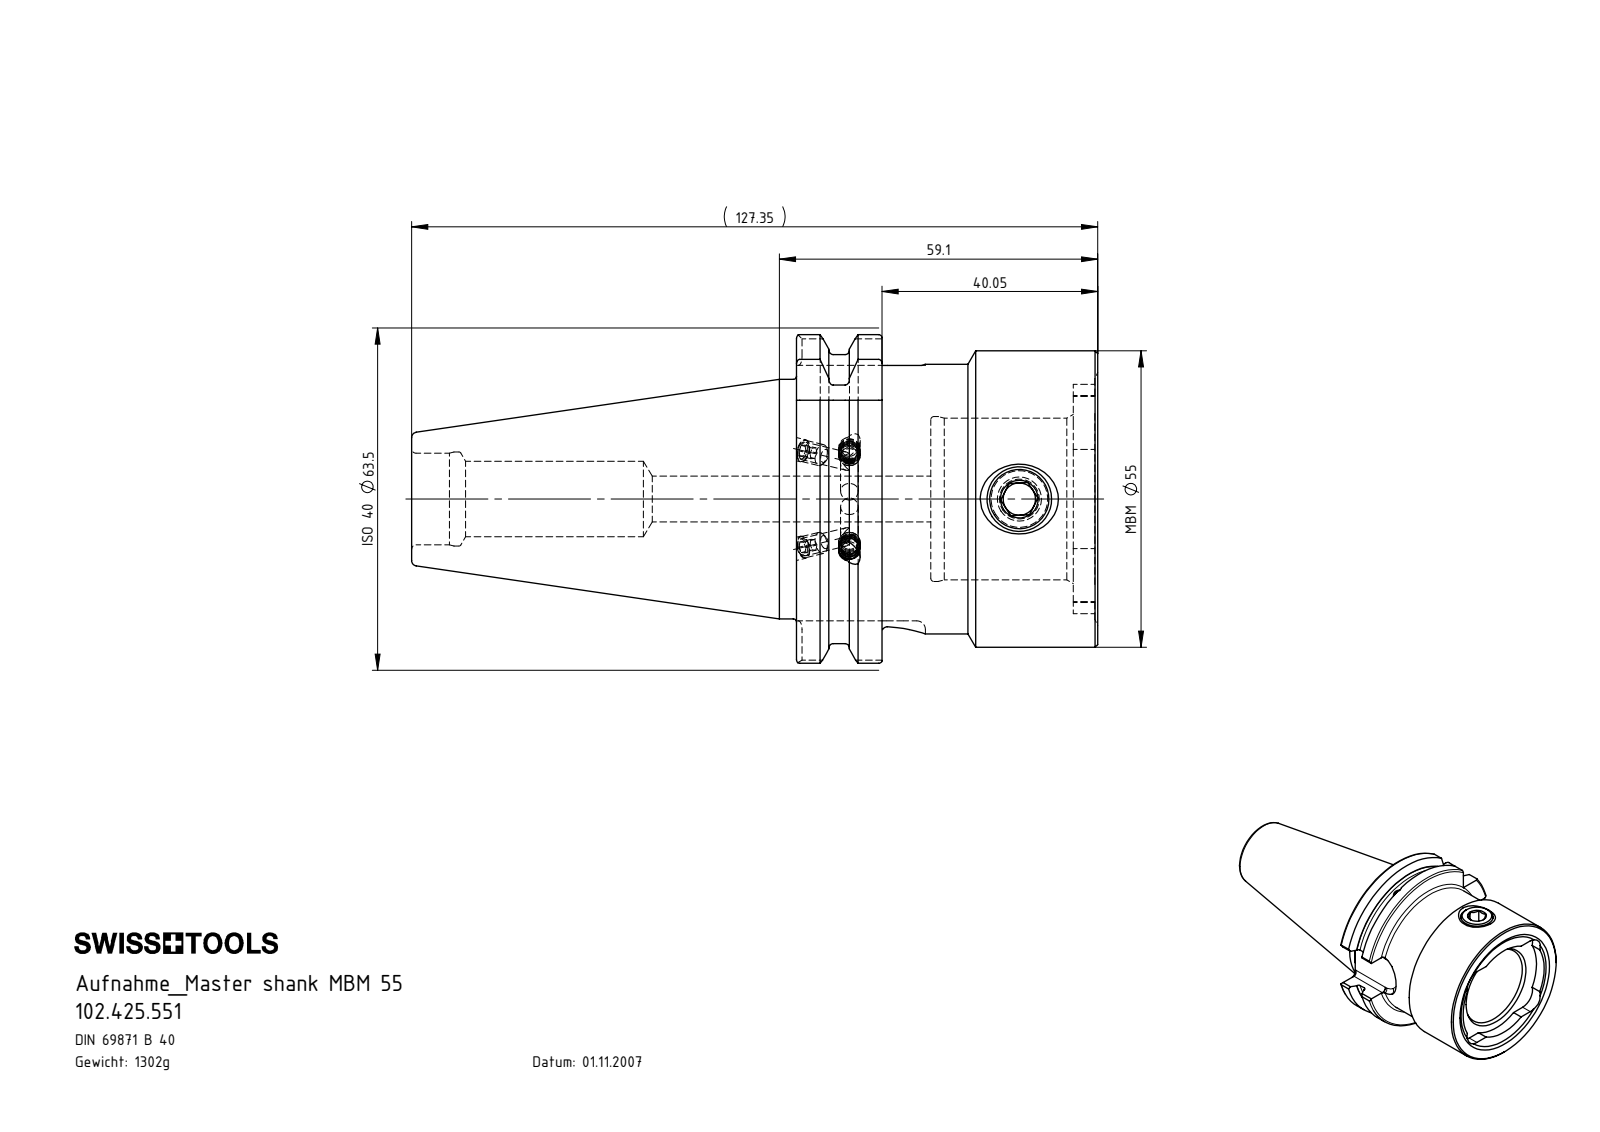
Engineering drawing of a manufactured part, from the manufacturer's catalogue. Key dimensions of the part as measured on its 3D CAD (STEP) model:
Part name (STEP PRODUCT): ISO 4026 - M4 x 5_PreviewCfg; 102.425.551; SB4-MB5.K01.059_D_mit Bundkhlung; MB5-ER1.001.017_A (+1 more)
STEP written by: SolidWorks 2017 (CONFIG_CONTROL_DESIGN)
Units: millimetres
Bodies: 8 solids, 314 faces (81 planar, 92 cylindrical, 141 other)
Overall size (bounding box): 127.35 × 63.5 × 60.94
Volume: 165 827 mm³ · Surface area: 32 288 mm²
Round holes (diameter × count): ⌀3.3 ×3, ⌀3 ×2, ⌀4.2 ×2, ⌀4 ×1, ⌀6 ×1, ⌀8.5 ×1, ⌀11 ×1, ⌀14 ×1, ⌀17 ×1, ⌀17.45 ×1, ⌀30 ×1, ⌀30.6 ×1
Round bosses / shafts (diameter × count): ⌀4 ×4, ⌀55 ×1, ⌀50 ×1, ⌀44.45 ×1, ⌀12 ×1
Partial cylindrical surfaces — rounded edges, fillets, slot ends (radius × count): R1.6 ×8, R5.2 ×4, R8 ×1, R8.05 ×1, R18.5 ×1, R21.27 ×1, R28 ×1, R31.75 ×1
Main face-to-face distances: 15.85, 24.9, 9.05, 55.9, 40.05, 31, 51.35, 35.5, 26.45, 4.55
